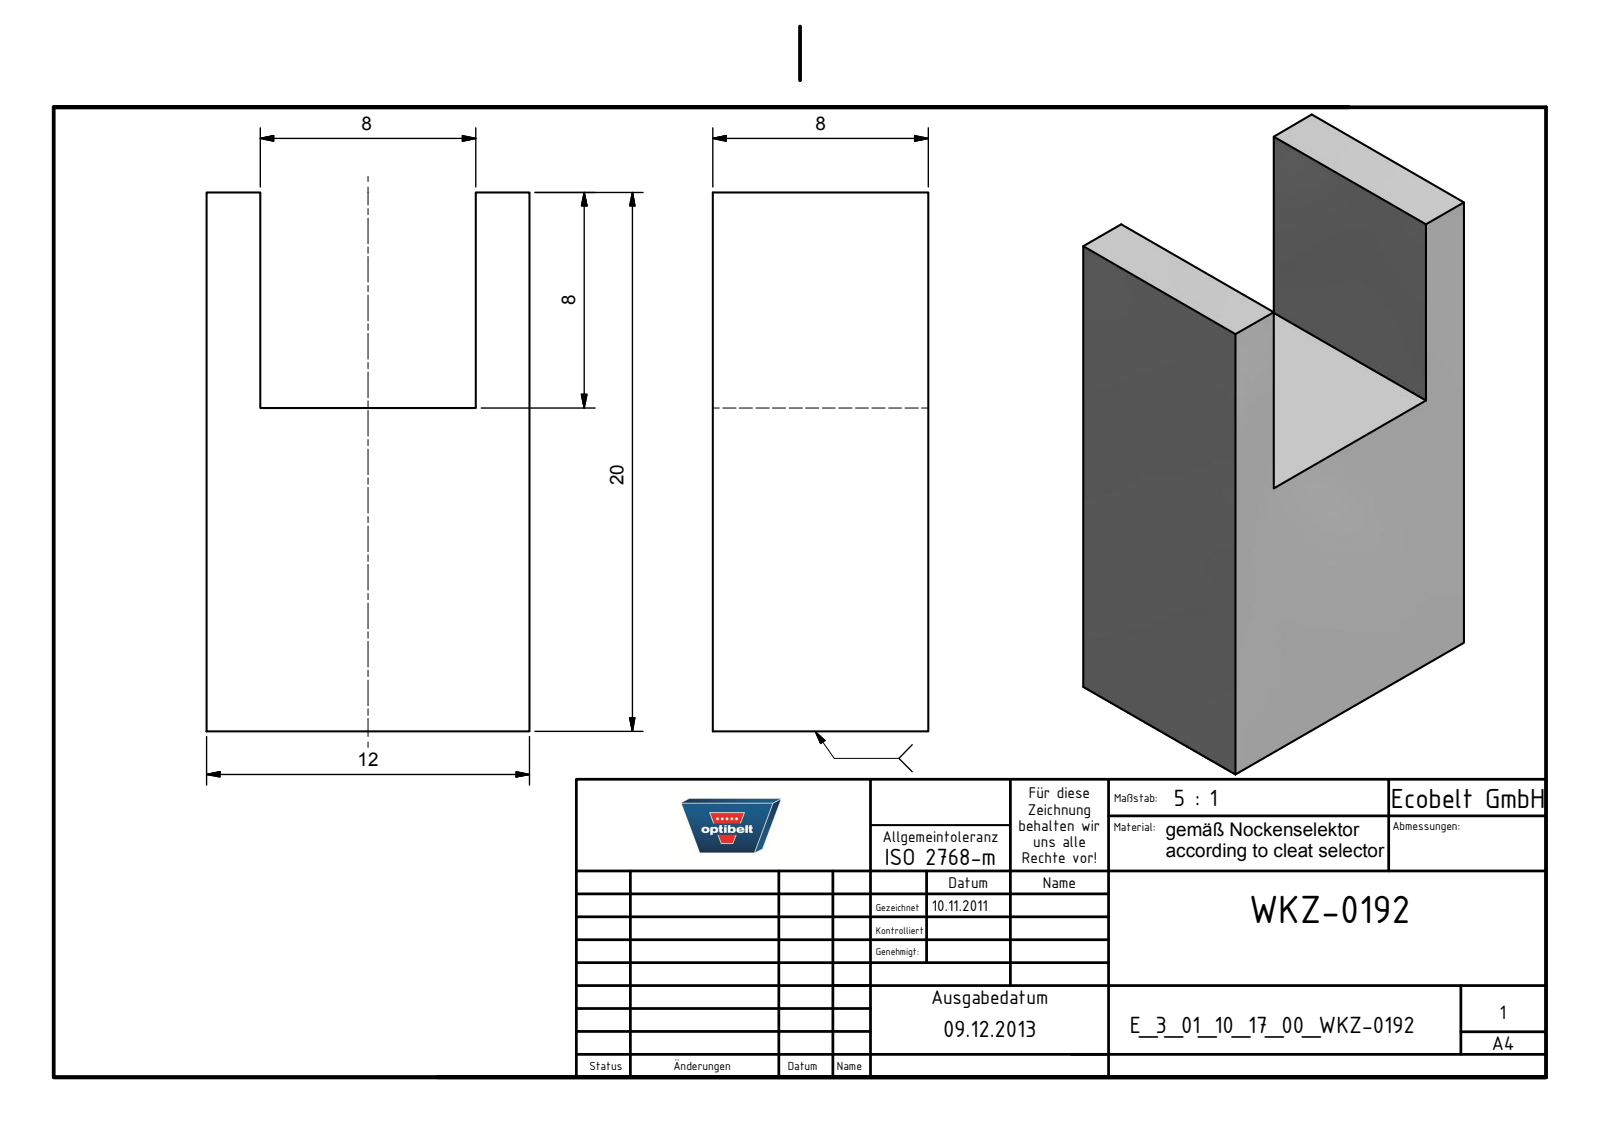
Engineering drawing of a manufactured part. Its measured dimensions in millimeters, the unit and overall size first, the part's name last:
Units: millimetres
Overall size (bounding box): 20 × 12 × 8
Main face-to-face distances: 8, 12, 2, 10, 20
Volume: 1 408 mm³ · Surface area: 992 mm²
Bodies: 1 solid, 10 faces (10 planar, 0 cylindrical, 0 other)
Part name (STEP PRODUCT): E_3_01_10_17_00_WKZ-0192
STEP written by: Autodesk Inventor 2025 (AUTOMOTIVE_DESIGN)
